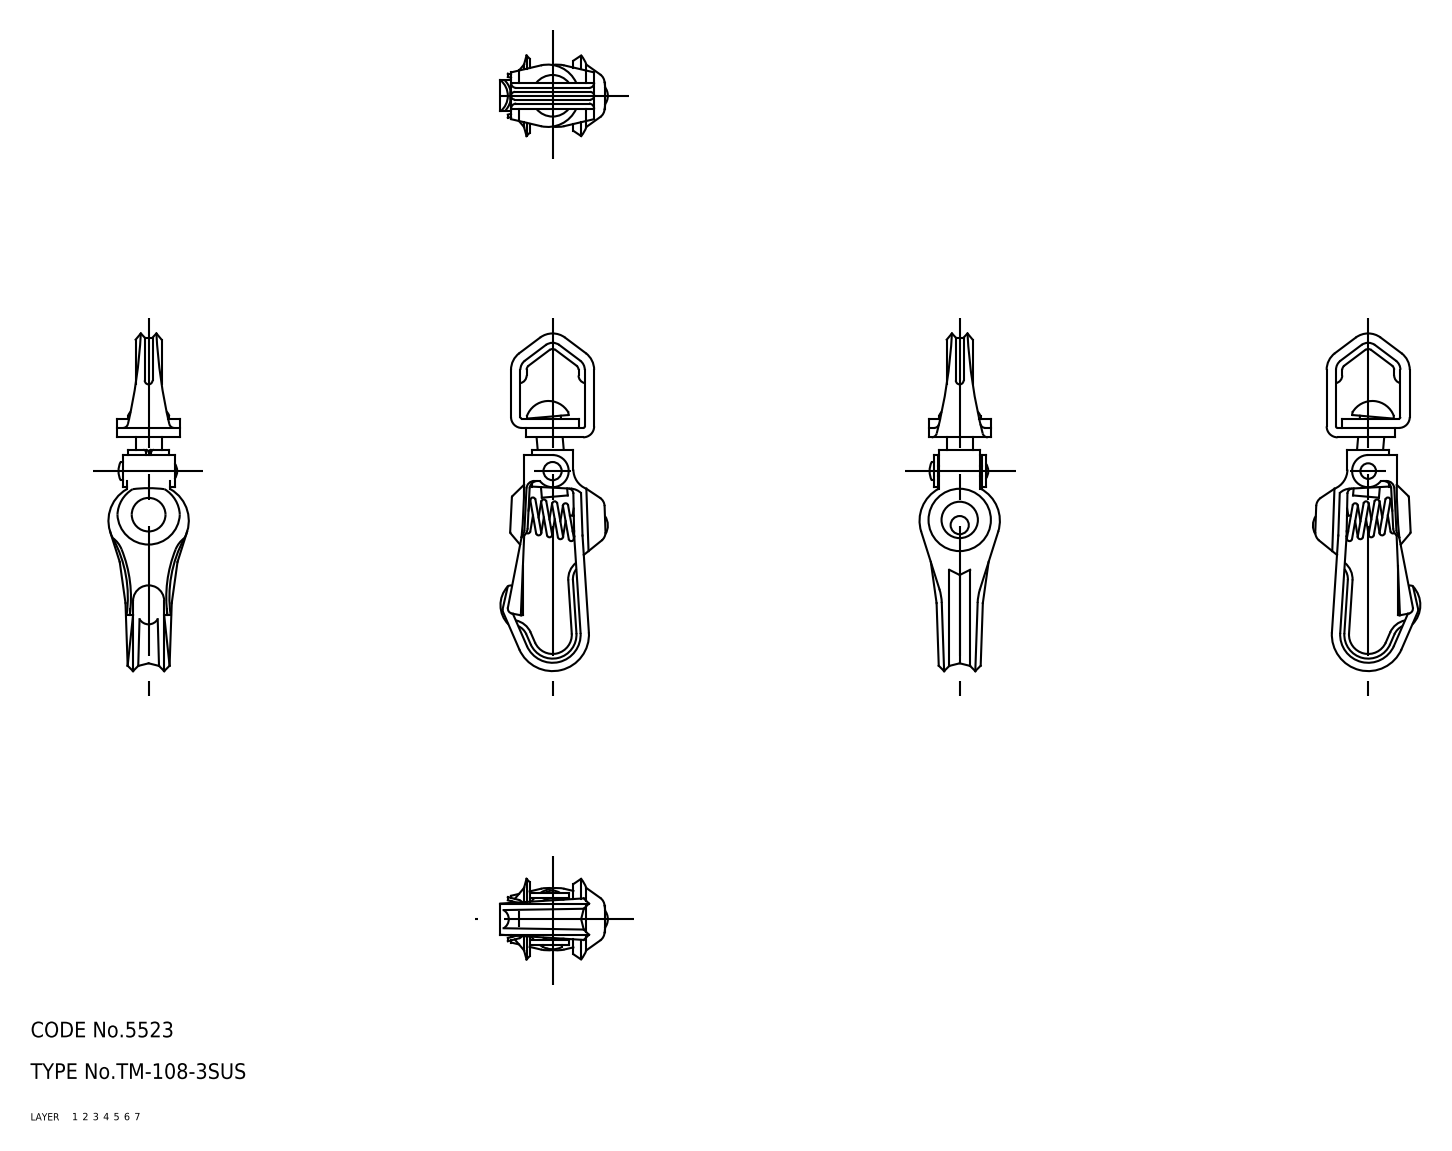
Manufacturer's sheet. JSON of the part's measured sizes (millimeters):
{"part_name": "spring; stopper; ring; pin_C (+4 more)", "step_written_by": "CADfix (AUTOMOTIVE_DESIGN)", "units": "millimeters", "bodies": {"solids": 7, "faces": 230, "planar": 0, "cylindrical": 0, "other": 230}, "overall_size": [65, 18.8, 15.6], "volume_mm3": 2756, "surface_area_mm2": 4712}
